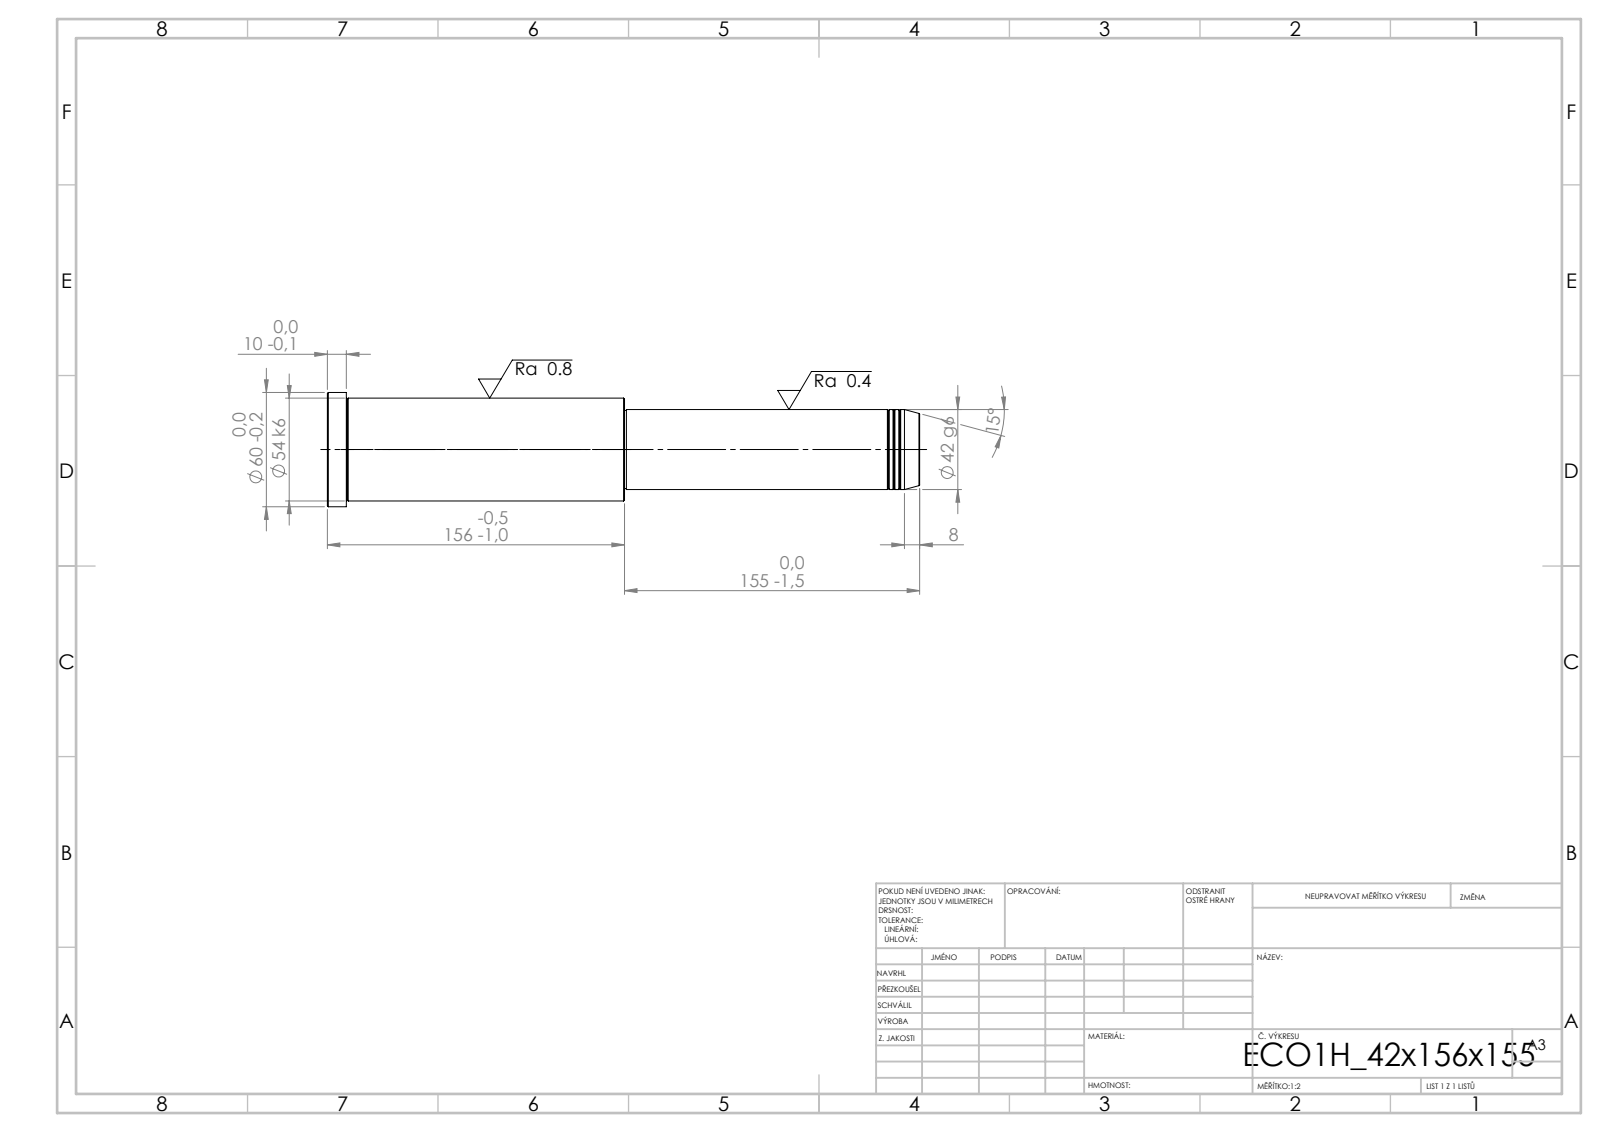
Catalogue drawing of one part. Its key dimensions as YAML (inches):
step_written_by: "SolidWorks 2019 (CONFIG_CONTROL_DESIGN)"
units: inches
bodies: {solids: 1, faces: 43, planar: 5, cylindrical: 14, other: 24}
overall_size: [12.244, 2.362, 2.362]
volume: 35.15
surface_area: 81.83
round_bosses_or_shafts:
  - {diameter: 2.362, count: 1}
  - {diameter: 2.126, count: 1}
  - {diameter: 1.654, count: 1}
  - {diameter: 1.614, count: 1}
face_to_face_distances: [12.244, 6.102, 6.142, 11.85, 5.748, 0.394, 6.063, 0.039, 5.787, 6.181]
